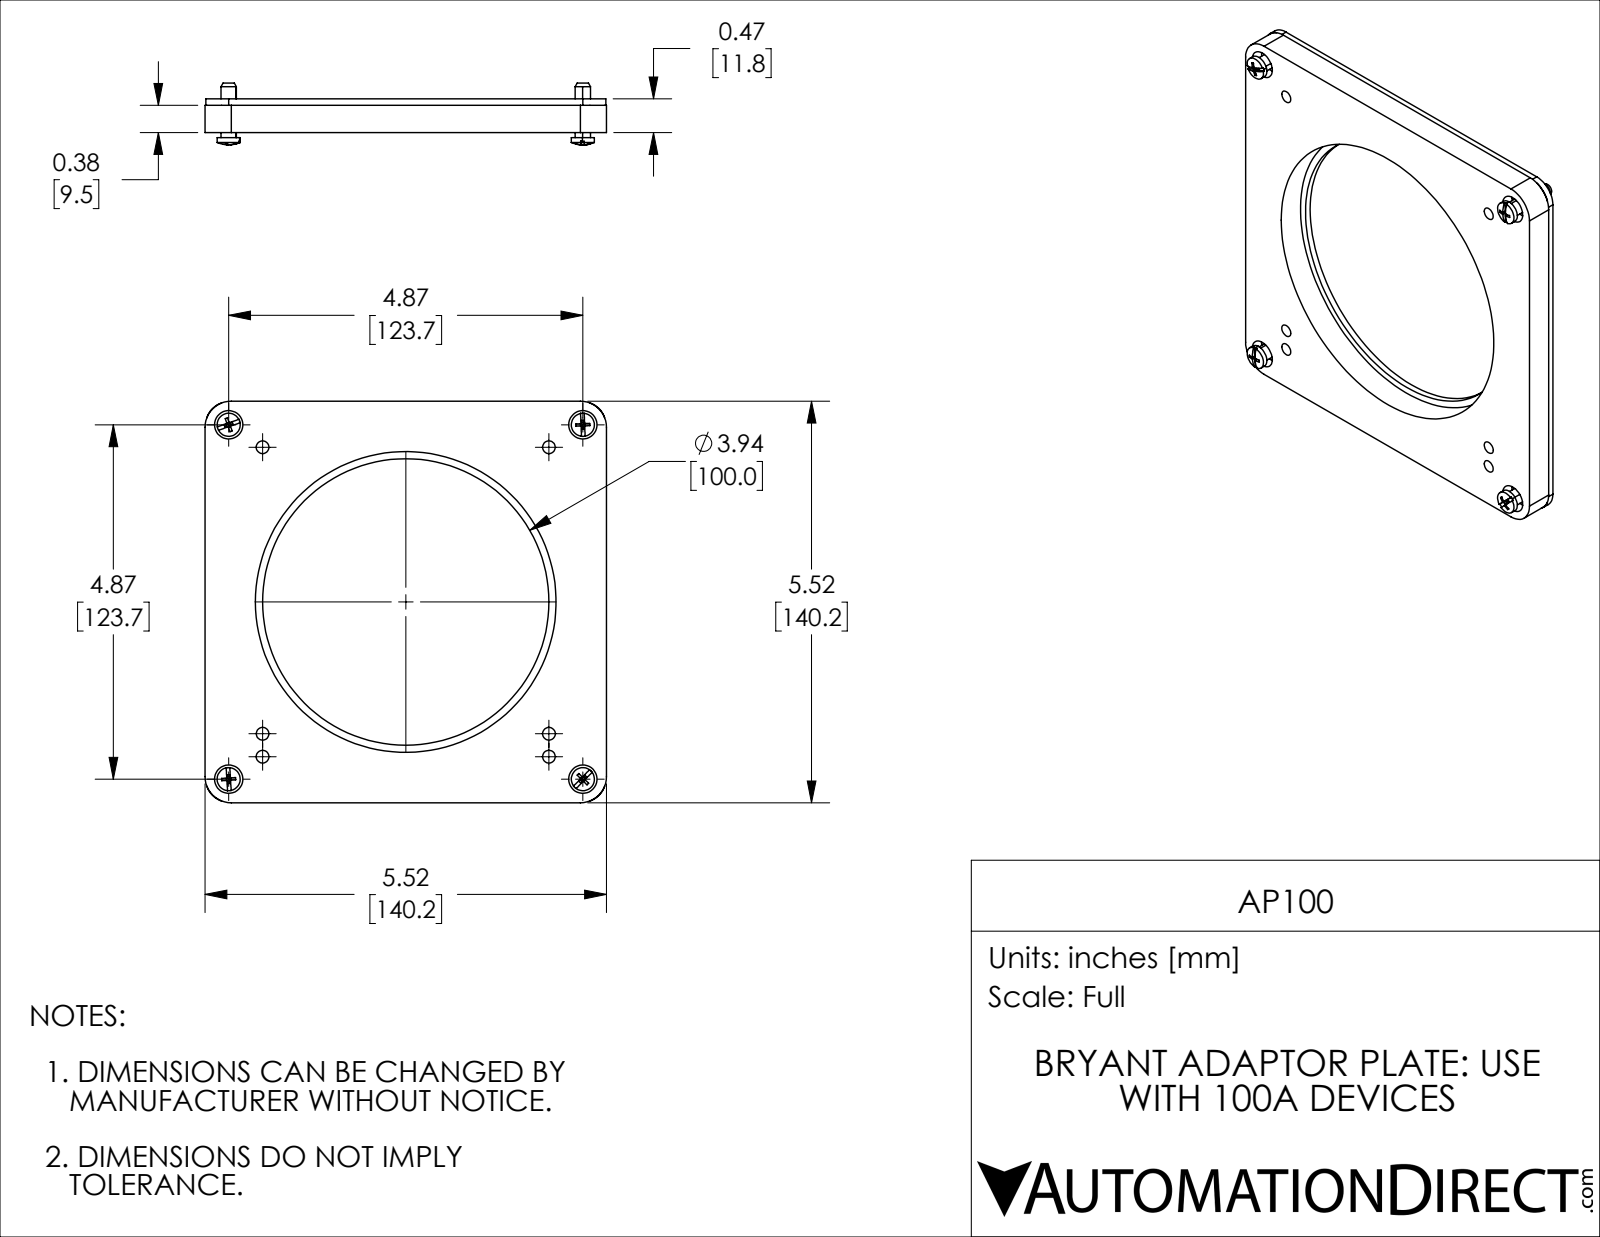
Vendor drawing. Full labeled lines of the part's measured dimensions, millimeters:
Part name (STEP PRODUCT): AP100
STEP written by: SolidWorks 2021 (CONFIG_CONTROL_DESIGN)
Units: millimetres
Bodies: 6 solids, 190 faces (102 planar, 72 cylindrical, 16 other)
Overall size (bounding box): 140.21 × 140.21 × 21.51
Volume: 129 183 mm³ · Surface area: 58 428 mm²
Round holes (diameter × count): ⌀4.45 ×6, ⌀5.56 ×4, ⌀5.59 ×4, ⌀8.51 ×4, ⌀9.91 ×4, ⌀100 ×1, ⌀105 ×1
Round bosses / shafts (diameter × count): ⌀8.08 ×4, ⌀5.38 ×4
Partial cylindrical surfaces — rounded edges, fillets, slot ends (radius × count): R7.98 ×4, R9.14 ×4
Main face-to-face distances: 2.29, 11.81, 9.52, 140.21, 139.96, 139.7, 139.95, 7.24, 4.95, 4.57
Hole centre spacings: 100, 123.76, 14.21, 161.03, 73.59, 100.32, 116.45, 116.52
